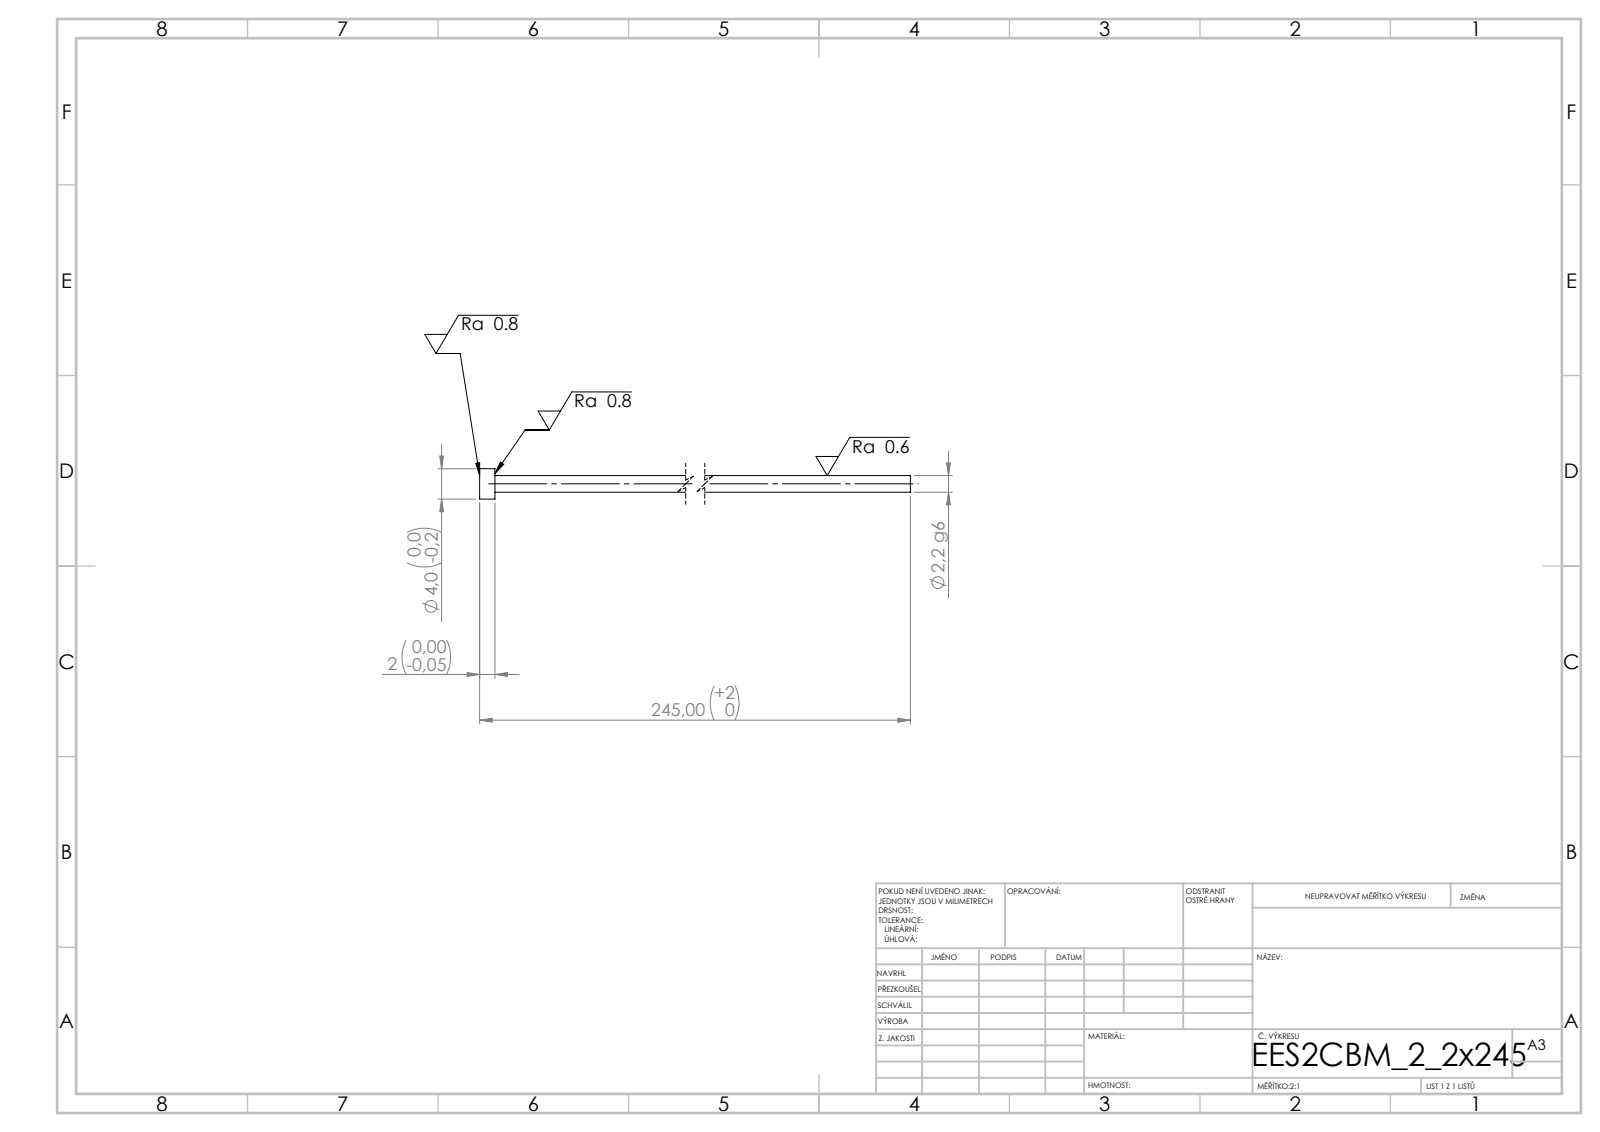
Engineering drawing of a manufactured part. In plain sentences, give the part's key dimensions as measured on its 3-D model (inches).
Its 3-D file was written by "SolidWorks 2019 (CONFIG_CONTROL_DESIGN)". It is 1 solid with 7 faces: 3 planar, 4 cylindrical and 0 other. Overall it measures 9.646 by 0.157 by 0.157 inches. Its volume is 0.058 cubic inches and its surface area 2.682 square inches. Round bosses or shafts: 1 of diameter 0.157, 1 of diameter 0.087. The main face-to-face distances are 0.079, 9.646, 9.567.
